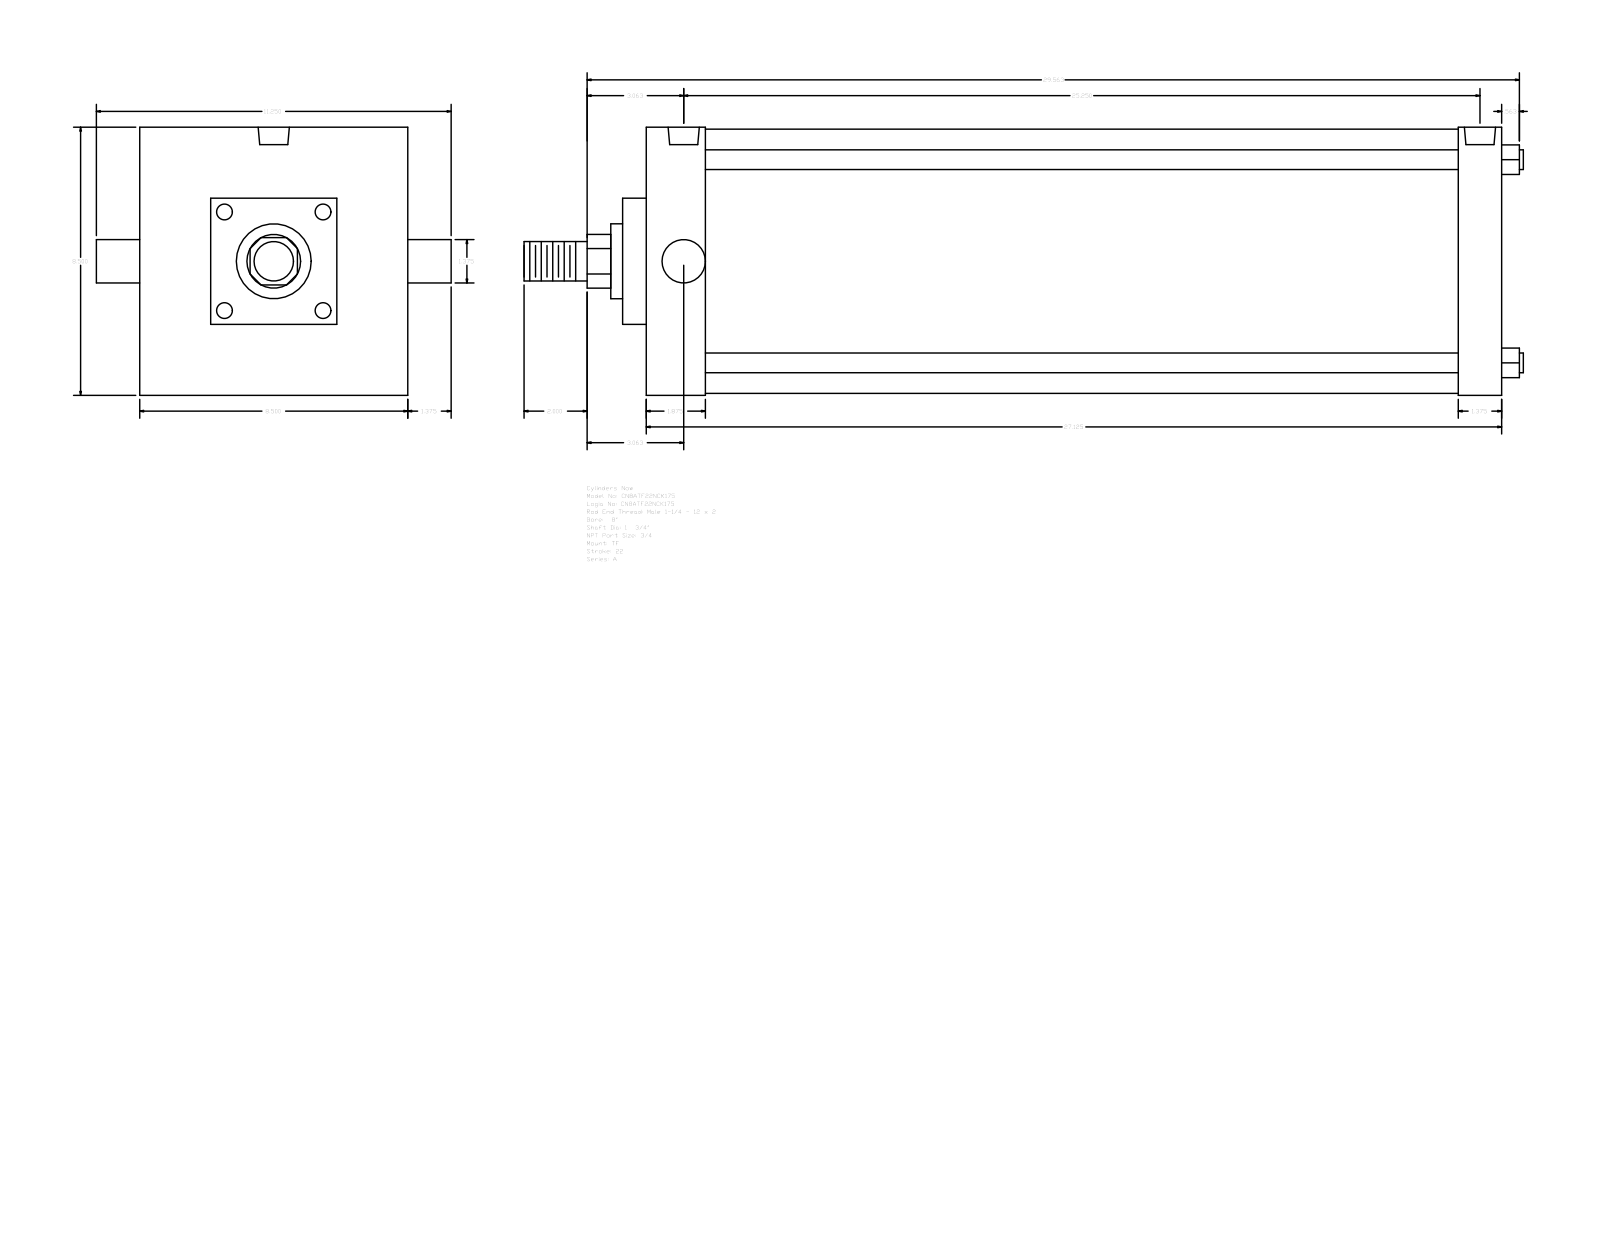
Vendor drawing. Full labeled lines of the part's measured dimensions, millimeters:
Part name (STEP PRODUCT): A_TF__0800_1.75
STEP written by: GSSL Pune (CONFIG_CONTROL_DESIGN)
Units: millimetres
Bodies: 0 solids, 89 faces (65 planar, 24 cylindrical, 0 other)
Overall size (bounding box): 804.86 × 285.75 × 215.9
Round holes (diameter × count): ⌀15.08 ×3, ⌀25.12 ×2
Round bosses / shafts (diameter × count): ⌀15.88 ×4, ⌀212.72 ×1, ⌀60.33 ×1, ⌀44.45 ×1, ⌀34.92 ×1, ⌀31.75 ×1
Partial cylindrical surfaces — rounded edges, fillets, slot ends (radius × count): R21.63 ×1
Main face-to-face distances: 688.98, 215.9, 34.93, 47.63, 641.35, 654.05, 606.42, 19.05, 57.15, 158.75
Hole centre spacings: 6.35, 635, 628.65, 641.35
